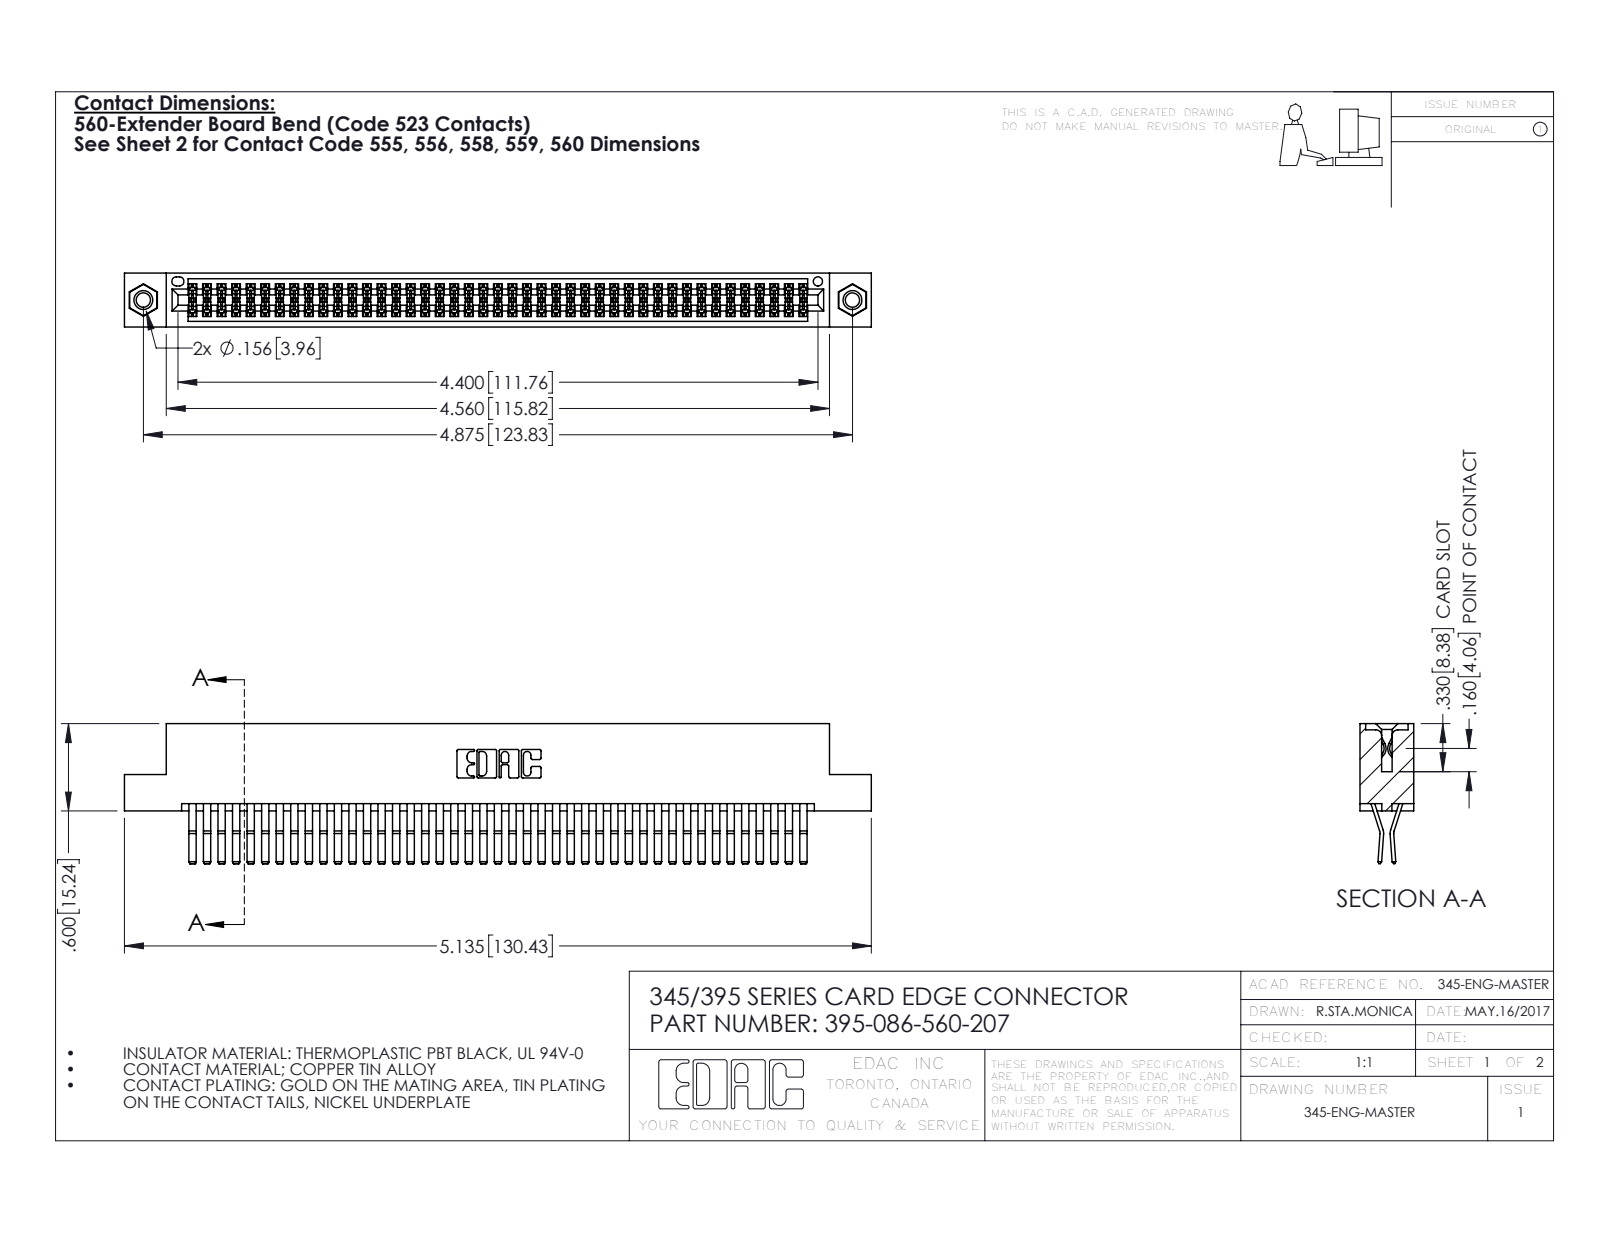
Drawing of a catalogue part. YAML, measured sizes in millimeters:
part_name: "345-292-001_560 Tail; 395-086-560-207; 345 Part_Flush Mounting Lugs - 0.156 Dia-TI; 345-250-001_345-250-005-103"
step_written_by: "SolidWorks 2016 (CONFIG_CONTROL_DESIGN)"
units: millimeters
bodies: {solids: 89, faces: 4658, planar: 2950, cylindrical: 1692, other: 16}
overall_size: [130.4, 24.4, 9.4]
volume: 13200
surface_area: 21050
round_holes:
  - {diameter: 2.5, count: 2}
  - {diameter: 3.2, count: 2}
  - {diameter: 4, count: 2}
  - {diameter: 1.6, count: 1}
round_bosses_or_shafts:
  - {diameter: 3.9, count: 2}
partial_cylinders:
  - {radius: 0.2, count: 130}
  - {radius: 0.3, count: 22}
  - {radius: 0.2, count: 6}
  - {radius: 0.8, count: 6}
  - {radius: 0.7, count: 3}
  - {radius: 0.3, count: 2}
  - {radius: 0.4, count: 2}
  - {radius: 0.5, count: 2}
face_to_face_distances: [0.6, 1.8, 7.6, 9.4, 5.1, 2.5, 6.9, 5.7, 4.4, 3.8]
hole_center_spacings: [6.9, 117.8, 123.8]
